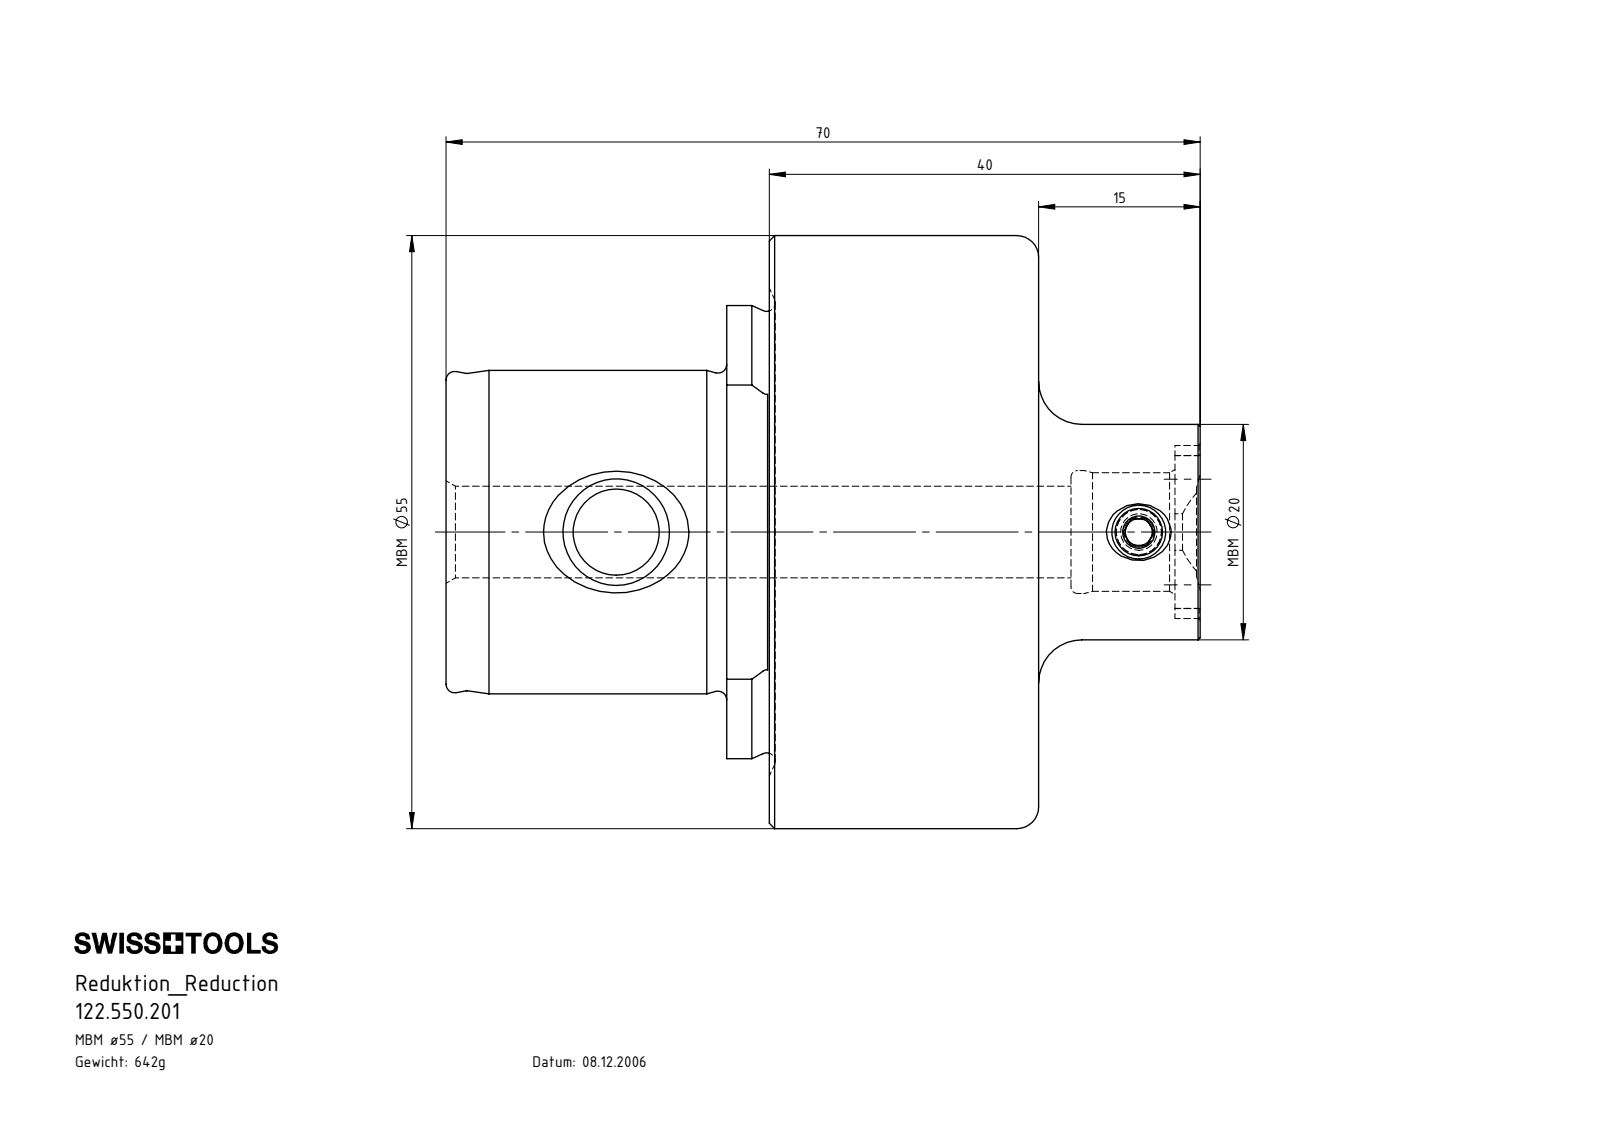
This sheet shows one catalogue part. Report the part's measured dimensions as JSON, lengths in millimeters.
{"part_name": "MB5-MB1.K01.040_C; MB1-ER1.001.006_A; 122.550.201", "step_written_by": "SolidWorks 2017 (CONFIG_CONTROL_DESIGN)", "units": "millimeters", "bodies": {"solids": 2, "faces": 135, "planar": 31, "cylindrical": 34, "other": 70}, "overall_size": [70, 55, 55], "volume_mm3": 81784, "surface_area_mm2": 14881, "round_holes": [[2.5, 1], [4.2, 1], [8, 1], [8.5, 1], [11, 1], [11.4, 1]], "round_bosses_or_shafts": [[55, 1], [30, 1], [20, 1], [5, 1]], "partial_cylinders_radius": [[2.2, 4], [6.5, 1], [8.03, 1], [21.02, 1]], "face_to_face_distances": [25, 30, 55, 26.05, 3.95, 28.95, 29.85, 3.8, 25.15, 32], "hole_center_spacings": [48.5]}
